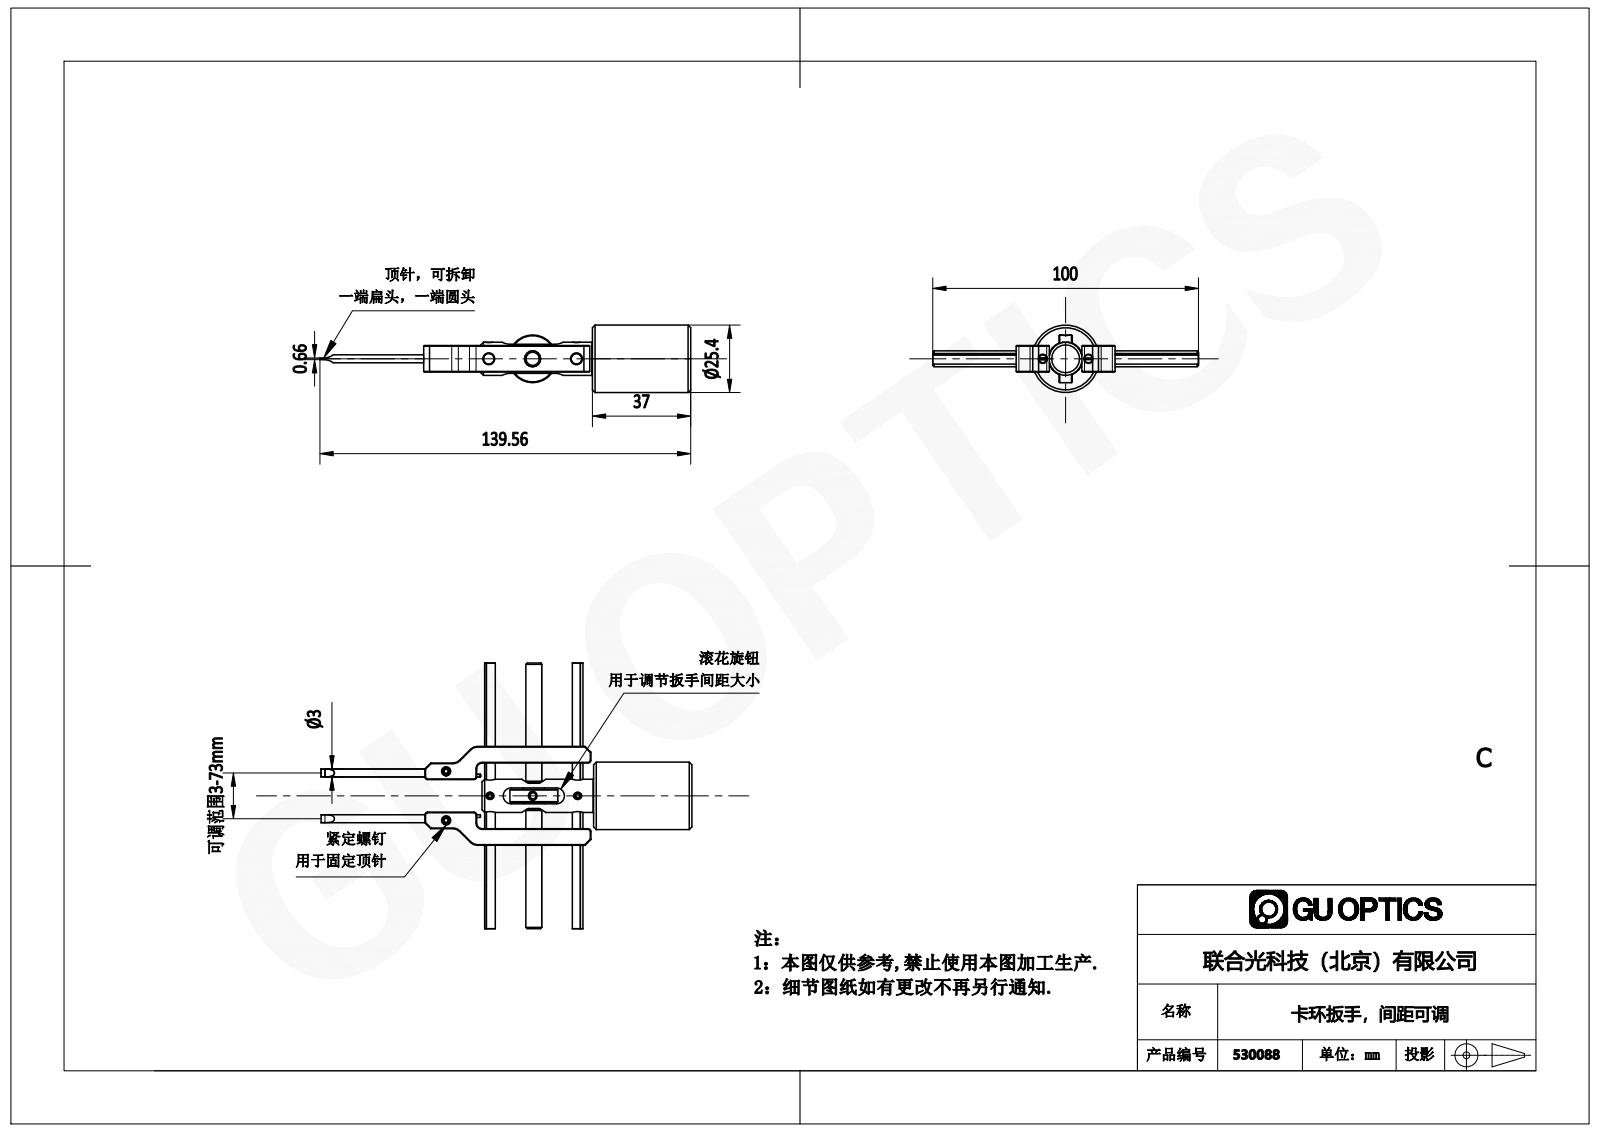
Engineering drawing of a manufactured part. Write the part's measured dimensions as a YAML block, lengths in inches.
part_name: "530088"
step_written_by: "SolidWorks 2020 (CONFIG_CONTROL_DESIGN)"
units: inches
bodies: {solids: 0, faces: 830, planar: 472, cylindrical: 251, other: 107}
overall_size: [5.512, 3.937, 0.787]
round_holes:
  - {diameter: 0.118, count: 2}
round_bosses_or_shafts:
  - {diameter: 0.118, count: 4}
  - {diameter: 0.157, count: 2}
  - {diameter: 0.039, count: 2}
  - {diameter: 0.63, count: 1}
  - {diameter: 0.394, count: 1}
  - {diameter: 0.236, count: 1}
  - {diameter: 0.189, count: 1}
  - {diameter: 0.081, count: 1}
partial_cylinders:
  - {radius: 0.03, count: 30}
  - {radius: 0.02, count: 22}
  - {radius: 0.079, count: 10}
  - {radius: 0.004, count: 4}
  - {radius: 0.069, count: 2}
  - {radius: 0.256, count: 1}
  - {radius: 0.394, count: 1}
face_to_face_distances: [0.315, 0.546, 1.26, 0.276, 0.984, 1.575, 0.669, 0.591, 0.945, 0.545]
hole_center_spacings: [0.591]
